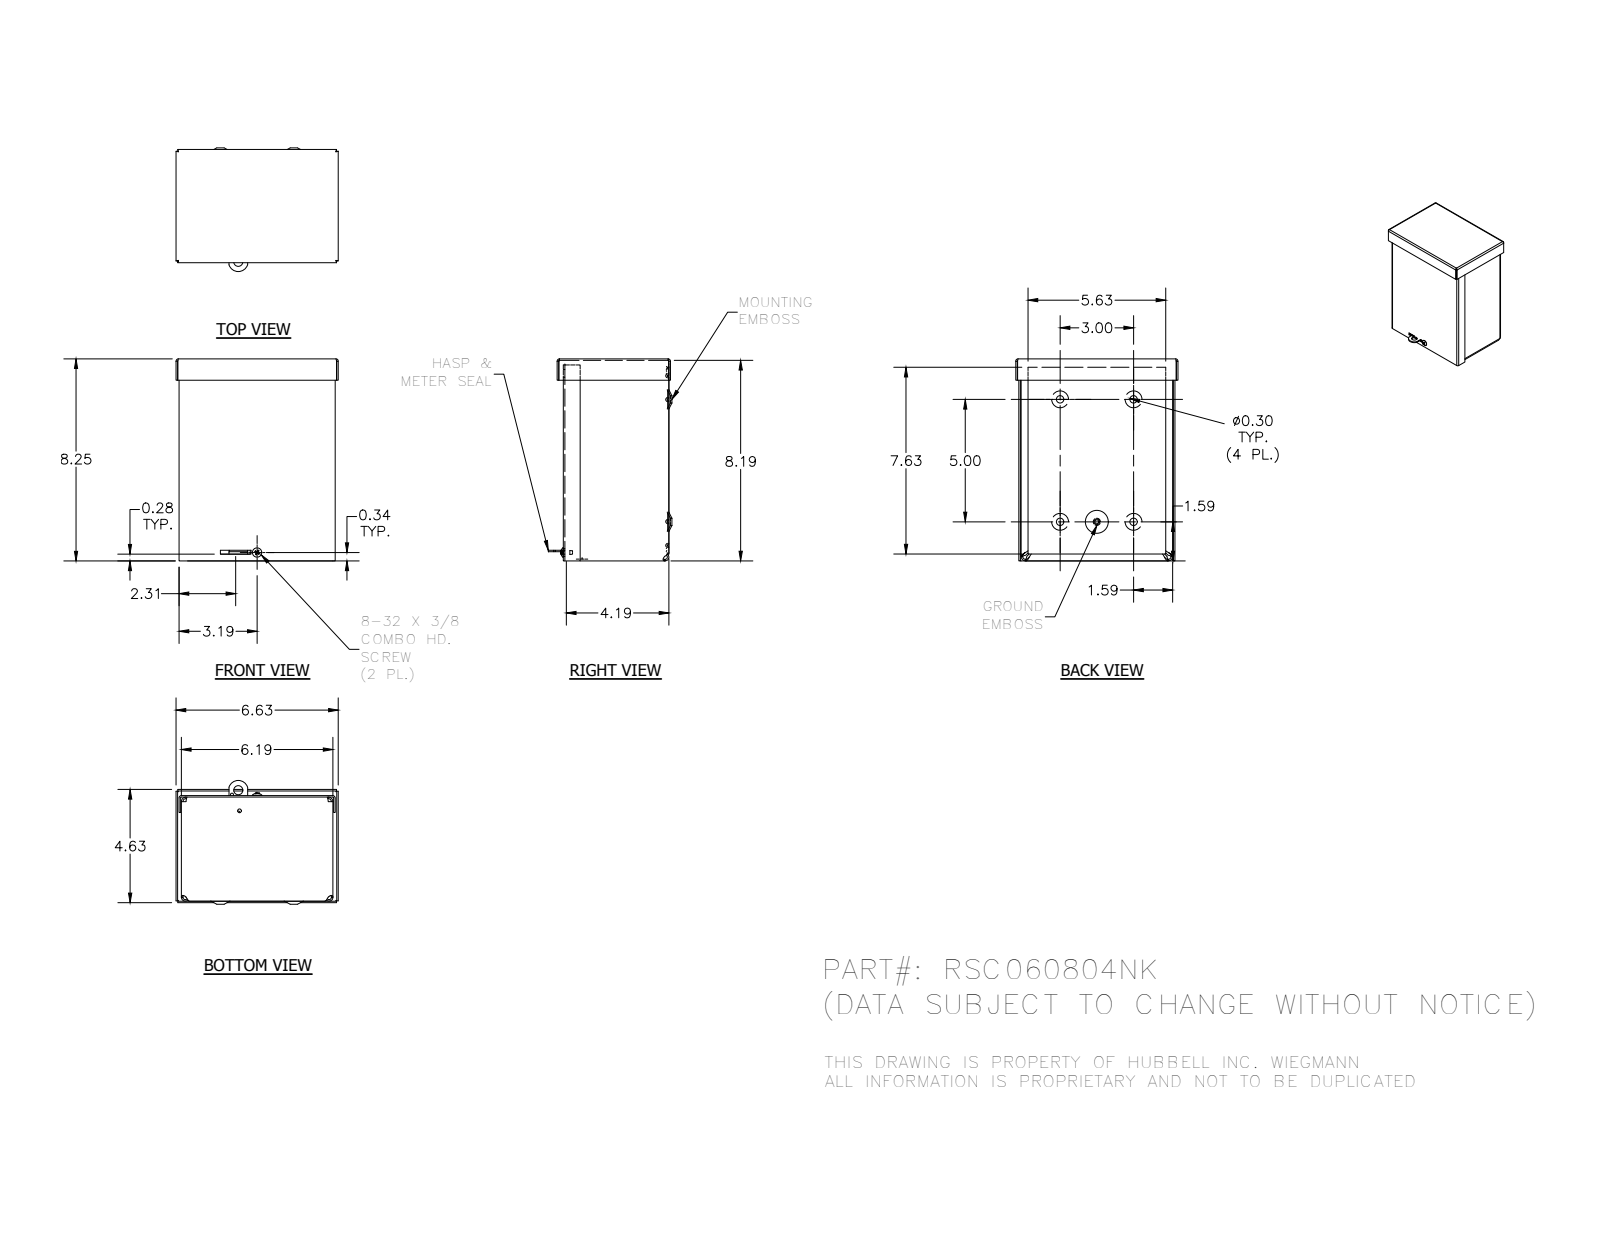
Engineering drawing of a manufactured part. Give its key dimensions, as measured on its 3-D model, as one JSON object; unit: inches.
{"part_name": "RSC060804NK_WRAP; RSC0608NK_LID; RSC0604NK_CAP; 3183 (+3 more)", "step_written_by": "Autodesk Inventor 2014 (AUTOMOTIVE_DESIGN)", "units": "inches", "bodies": {"solids": 6, "faces": 347, "planar": 153, "cylindrical": 73, "other": 121}, "overall_size": [8.25, 6.625, 5.125], "volume_in3": 19.1, "surface_area_in2": 627.3, "round_holes": [[0.3, 4], [0.313, 2], [0.125, 1], [0.136, 1], [0.148, 1], [0.156, 1], [0.165, 1], [0.375, 1]], "round_bosses_or_shafts": [[0.384, 1], [0.228, 1], [0.164, 1]], "partial_cylinders_radius": [[0.031, 8], [0.093, 8], [0.125, 8], [0.187, 8], [0.055, 4], [0.062, 4], [0.094, 4], [0.117, 4]], "face_to_face_distances": [0.062, 0.062, 6.126, 4.249, 4.187, 8.126, 0.063, 0.124, 4.312, 4.25], "hole_center_spacings": [1.5, 3, 5, 5.22, 5.831, 0.312, 0.777, 0.913]}
